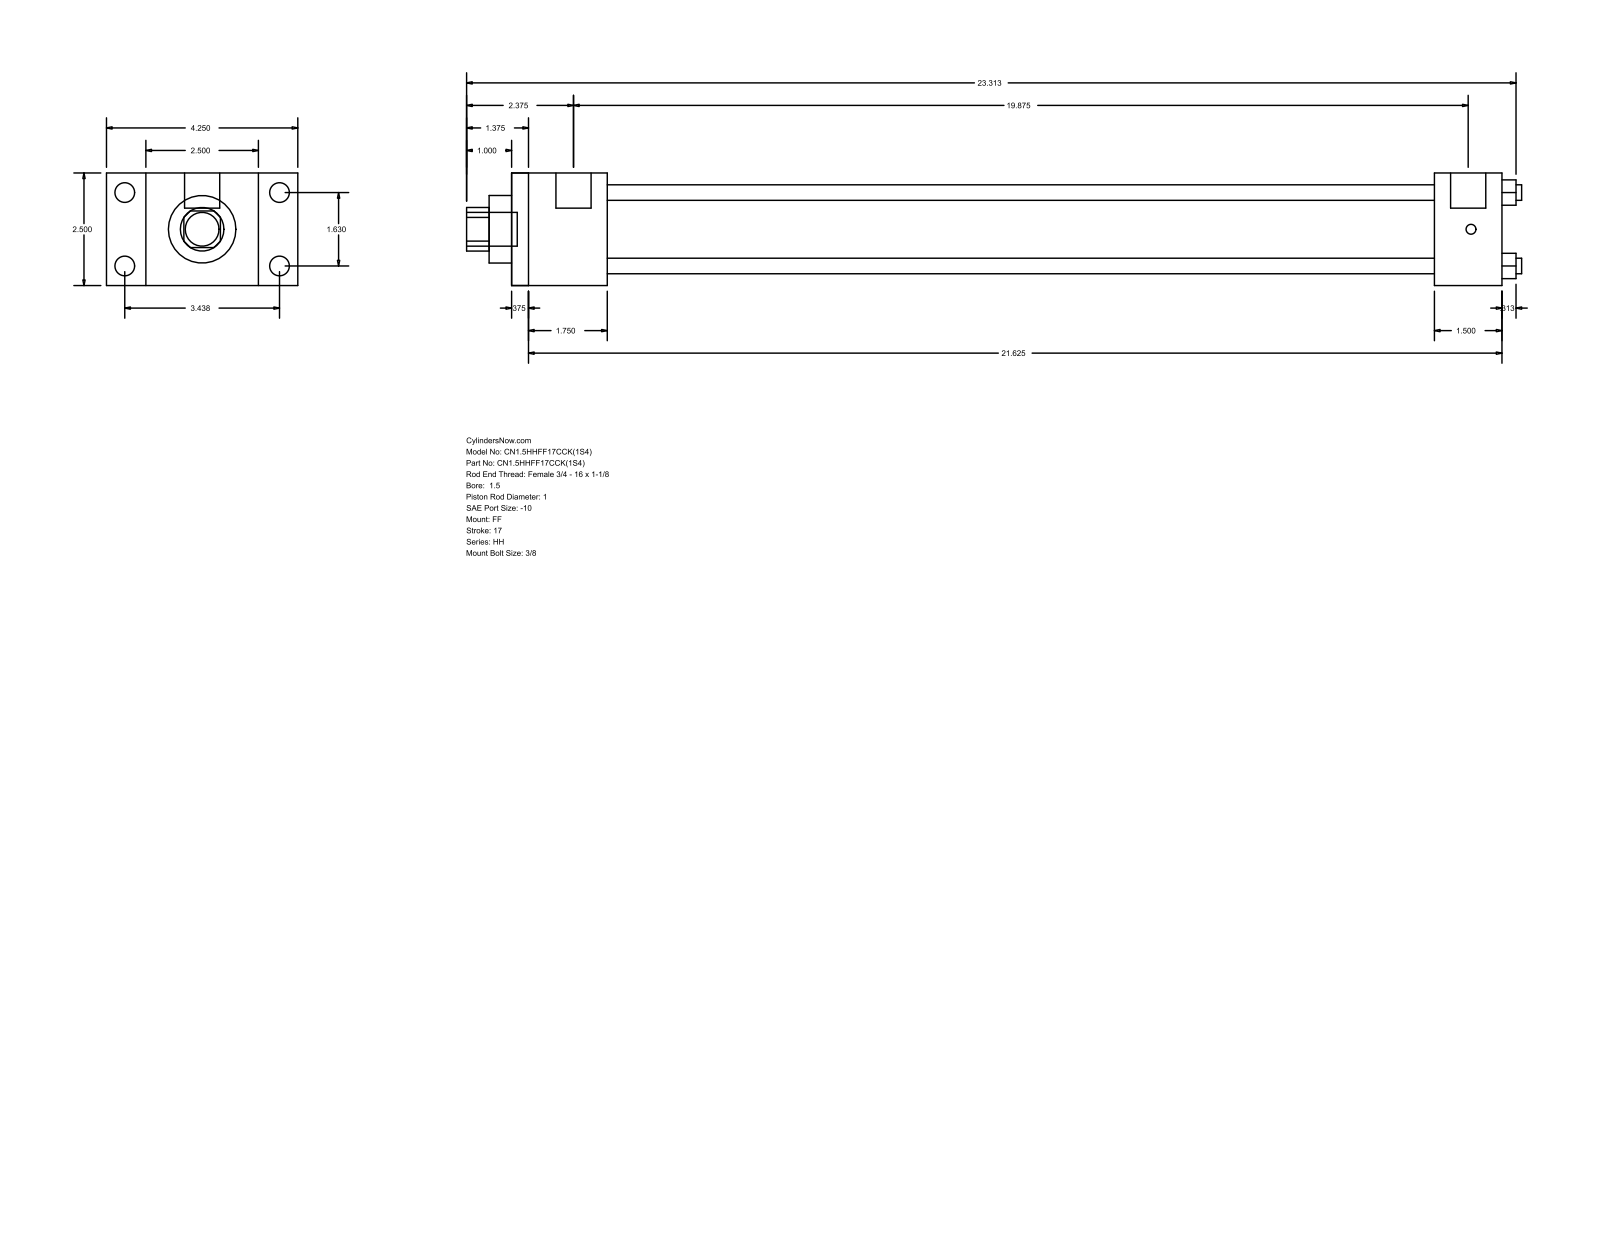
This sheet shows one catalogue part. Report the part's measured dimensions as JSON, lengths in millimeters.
{"part_name": "HH_FF__0150_1", "step_written_by": "GSSL Pune (CONFIG_CONTROL_DESIGN)", "units": "millimeters", "bodies": {"solids": 0, "faces": 92, "planar": 64, "cylindrical": 28, "other": 0}, "overall_size": [595.31, 107.95, 63.5], "round_holes": [[8.76, 4], [25.4, 1], [38.1, 1], [44.45, 1]], "round_bosses_or_shafts": [[11.13, 4], [5.56, 4], [19.84, 2], [19.05, 1]], "partial_cylinders_radius": [[12.29, 1]], "face_to_face_distances": [63.5, 558.8, 9.52, 549.28, 53.98, 44.46, 504.82, 520.7, 511.18, 466.72], "hole_center_spacings": [29.27, 41.4, 58.55]}
